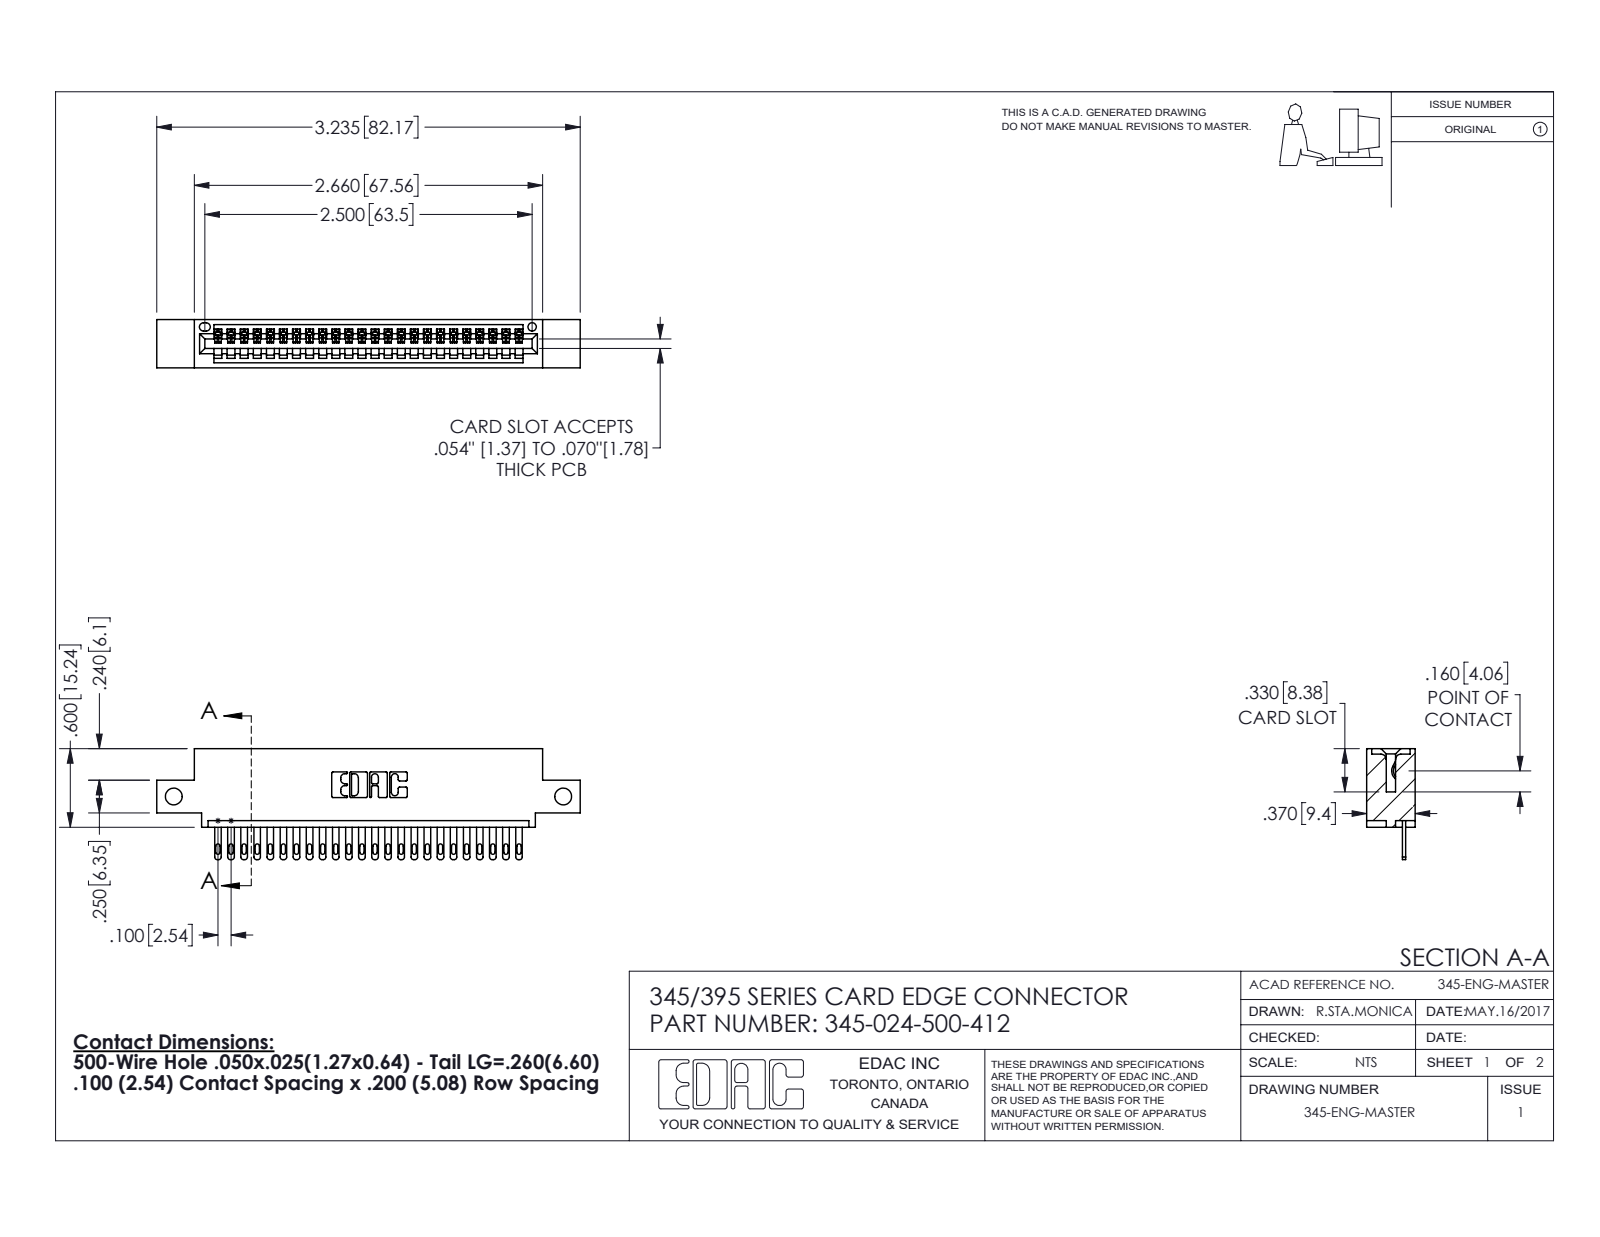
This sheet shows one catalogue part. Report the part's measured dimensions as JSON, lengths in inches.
{"part_name": "345 Part_0.110 Offset - Side Mount; 345-292-001_345-293-100; 345-024-500-412", "step_written_by": "SolidWorks 2016 (CONFIG_CONTROL_DESIGN)", "units": "inches", "bodies": {"solids": 25, "faces": 1426, "planar": 900, "cylindrical": 526, "other": 0}, "overall_size": [3.235, 0.847, 0.37], "volume_in3": 0.458, "surface_area_in2": 15.08, "round_holes": [[0.128, 2], [0.064, 1]], "partial_cylinders_radius": [[0.006, 48], [0.016, 48], [0.02, 48], [0.01, 22], [0.007, 6], [0.031, 6], [0.026, 3], [0.031, 2]], "face_to_face_distances": [0.298, 0.072, 0.37, 0.2, 0.098, 0.272, 0.025, 0.225, 0.149, 0.072], "hole_center_spacings": [2.975]}
